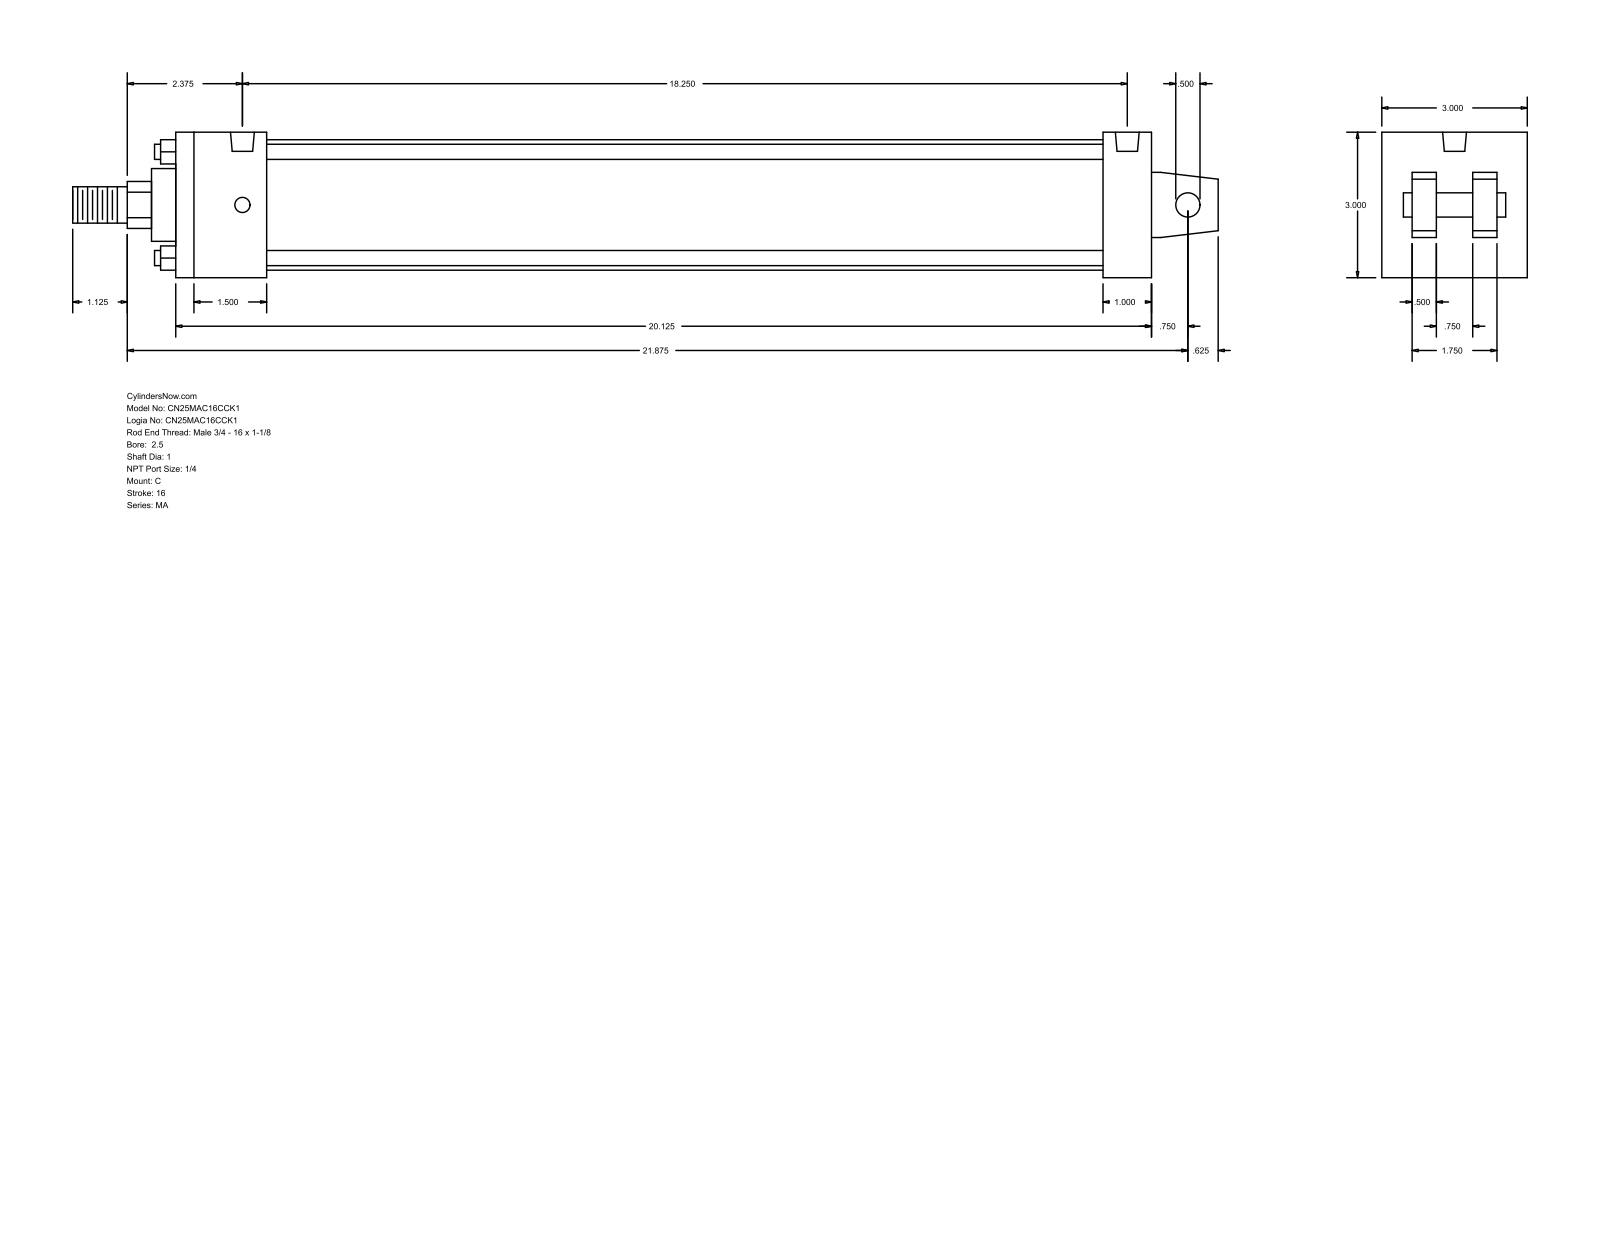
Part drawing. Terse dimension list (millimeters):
name: MA_C__0250_1
written by: GSSL Pune (CONFIG_CONTROL_DESIGN)
unit: mm
bodies: 0 solids, 103 faces (76 planar, 27 cylindrical, 0 other)
size: 600.08 × 76.2 × 76.2
holes: 4× ⌀7.94, 2× ⌀12.49
bosses: 4× ⌀7.94, 1× ⌀68.33, 1× ⌀38.1, 1× ⌀25.4, 1× ⌀19.05, 1× ⌀12.7
rounds: 1× R12.29
face distances: 76.2, 511.18, 47.63, 12.7, 60.33, 15.87, 25.4, 28.57, 485.78, 438.15
hole spacings: 463.55
